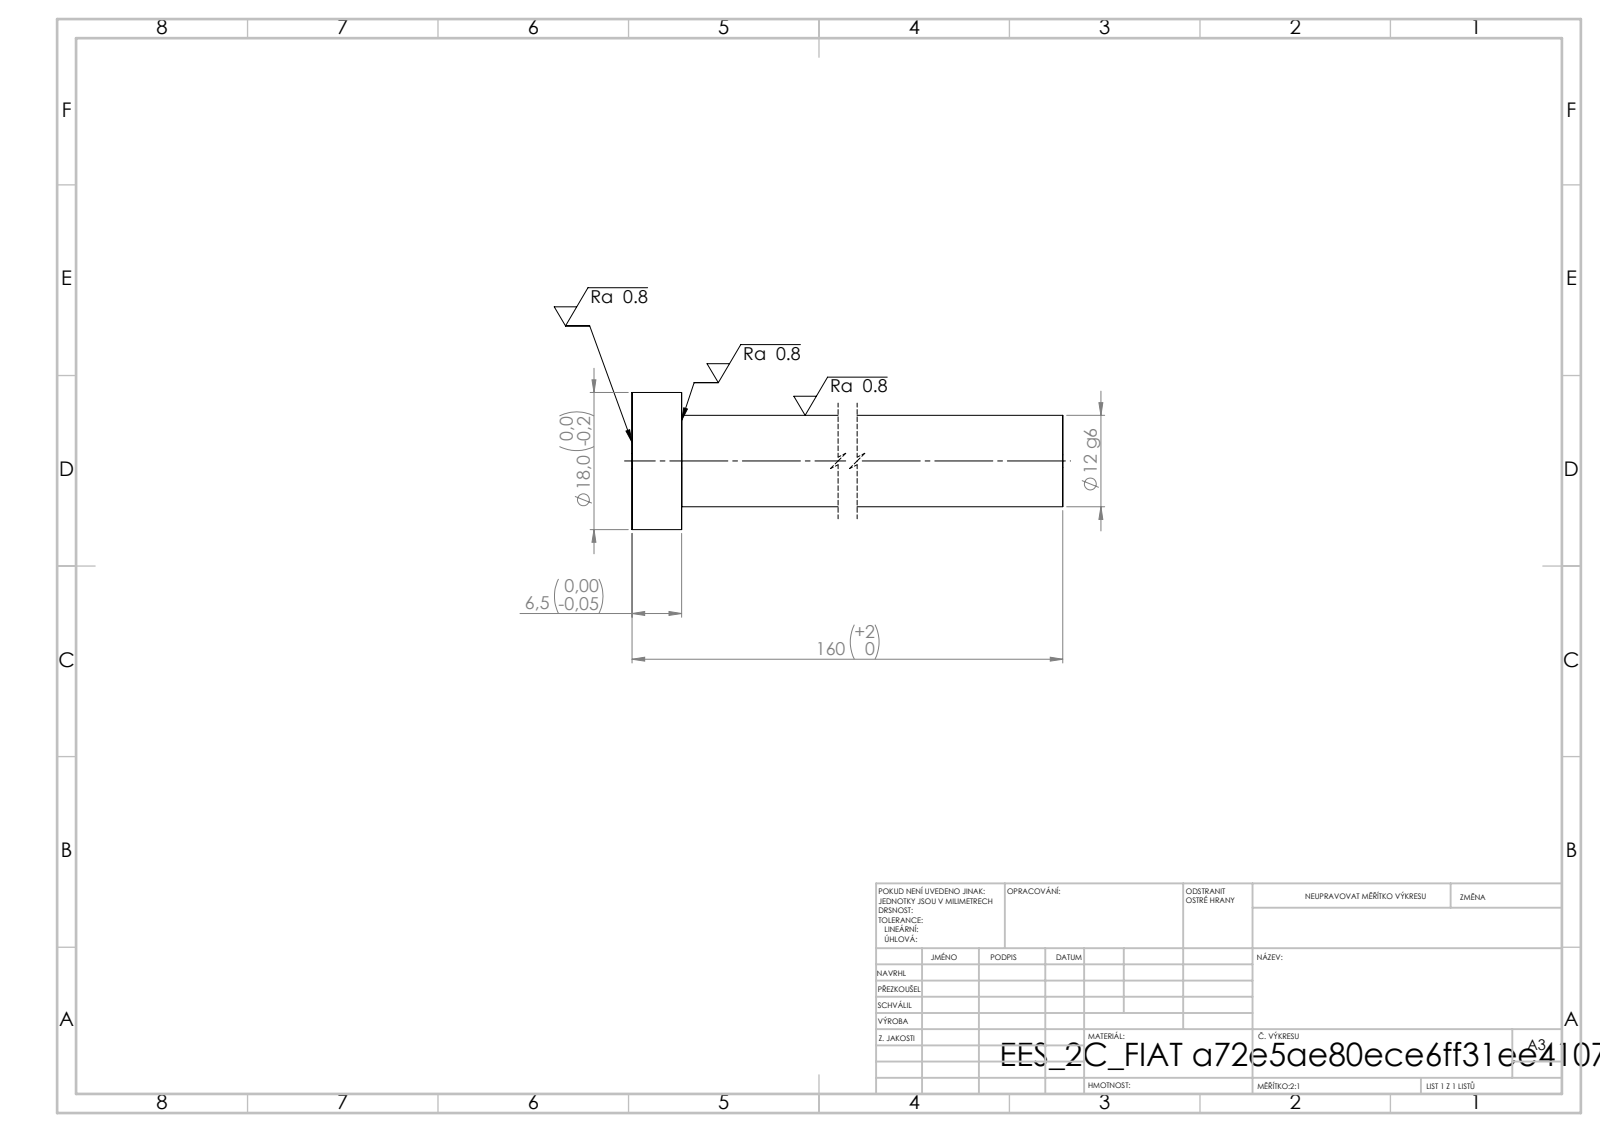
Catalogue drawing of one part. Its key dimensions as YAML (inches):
step_written_by: "SolidWorks 2019 (CONFIG_CONTROL_DESIGN)"
units: inches
bodies: {solids: 1, faces: 7, planar: 3, cylindrical: 4, other: 0}
overall_size: [6.299, 0.709, 0.709]
volume: 1.16
surface_area: 10.33
round_bosses_or_shafts:
  - {diameter: 0.709, count: 1}
  - {diameter: 0.472, count: 1}
face_to_face_distances: [0.256, 6.299, 6.043]
